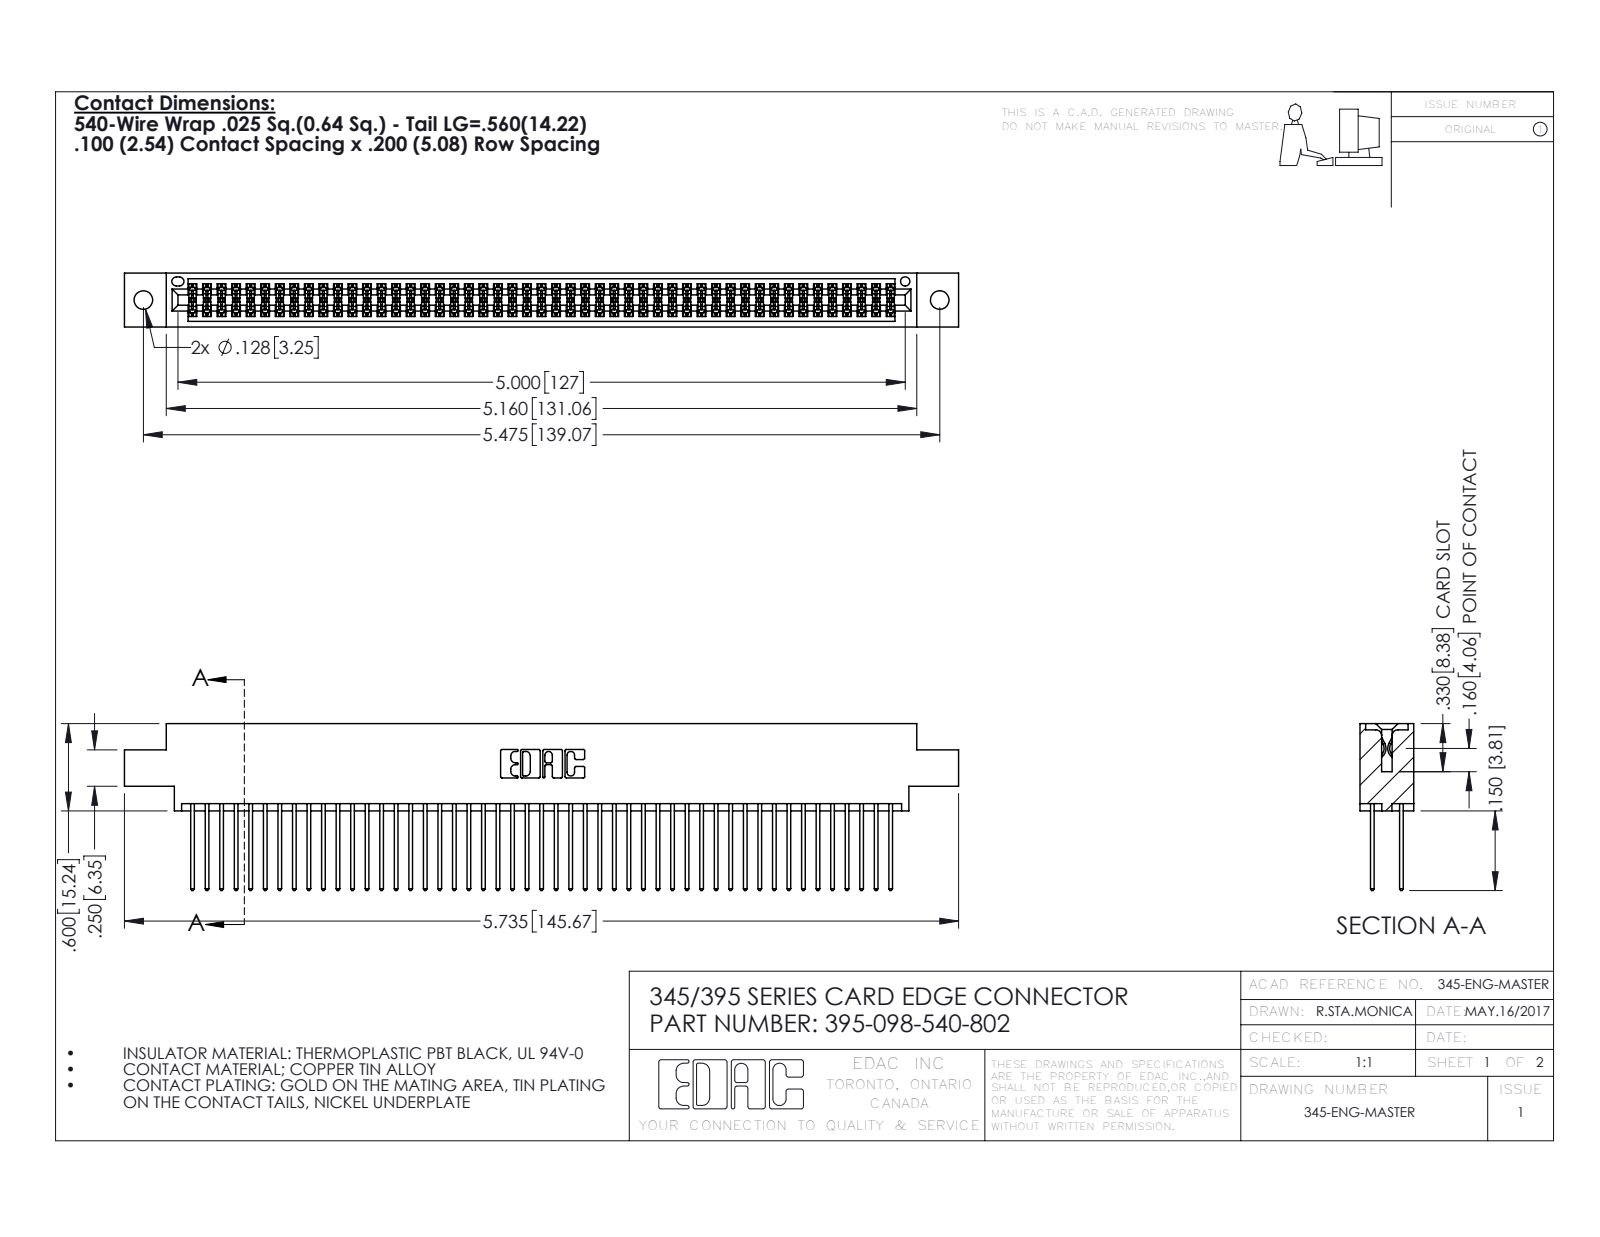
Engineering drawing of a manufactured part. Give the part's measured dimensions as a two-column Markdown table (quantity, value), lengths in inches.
| quantity | value |
| --- | --- |
| part name | 345-292-001_345-293-140; 345 Part_0.170 Offset - 0.128 Dia; 395-098-540-802 |
| STEP written by | SolidWorks 2016 (CONFIG_CONTROL_DESIGN) |
| units | inches |
| bodies | 99 solids, 5030 faces (3318 planar, 1712 cylindrical, 0 other) |
| overall size | 5.735 × 1.147 × 0.37 |
| volume | 0.881 in³ |
| surface area | 35.76 in² |
| round holes (diameter × count) | 0.128 × 2, 0.064 × 1 |
| partial cylindrical surfaces (radius × count) | 0.006 × 147, 0.01 × 98, 0.01 × 22, 0.007 × 6, 0.031 × 6, 0.026 × 3, 0.014 × 2, 0.019 × 2 |
| main face-to-face distances | 0.072, 0.298, 0.2, 0.098, 0.272, 0.025, 0.37, 0.225, 0.175, 0.149 |
| hole center spacings | 0.27, 5.239, 5.475 |
